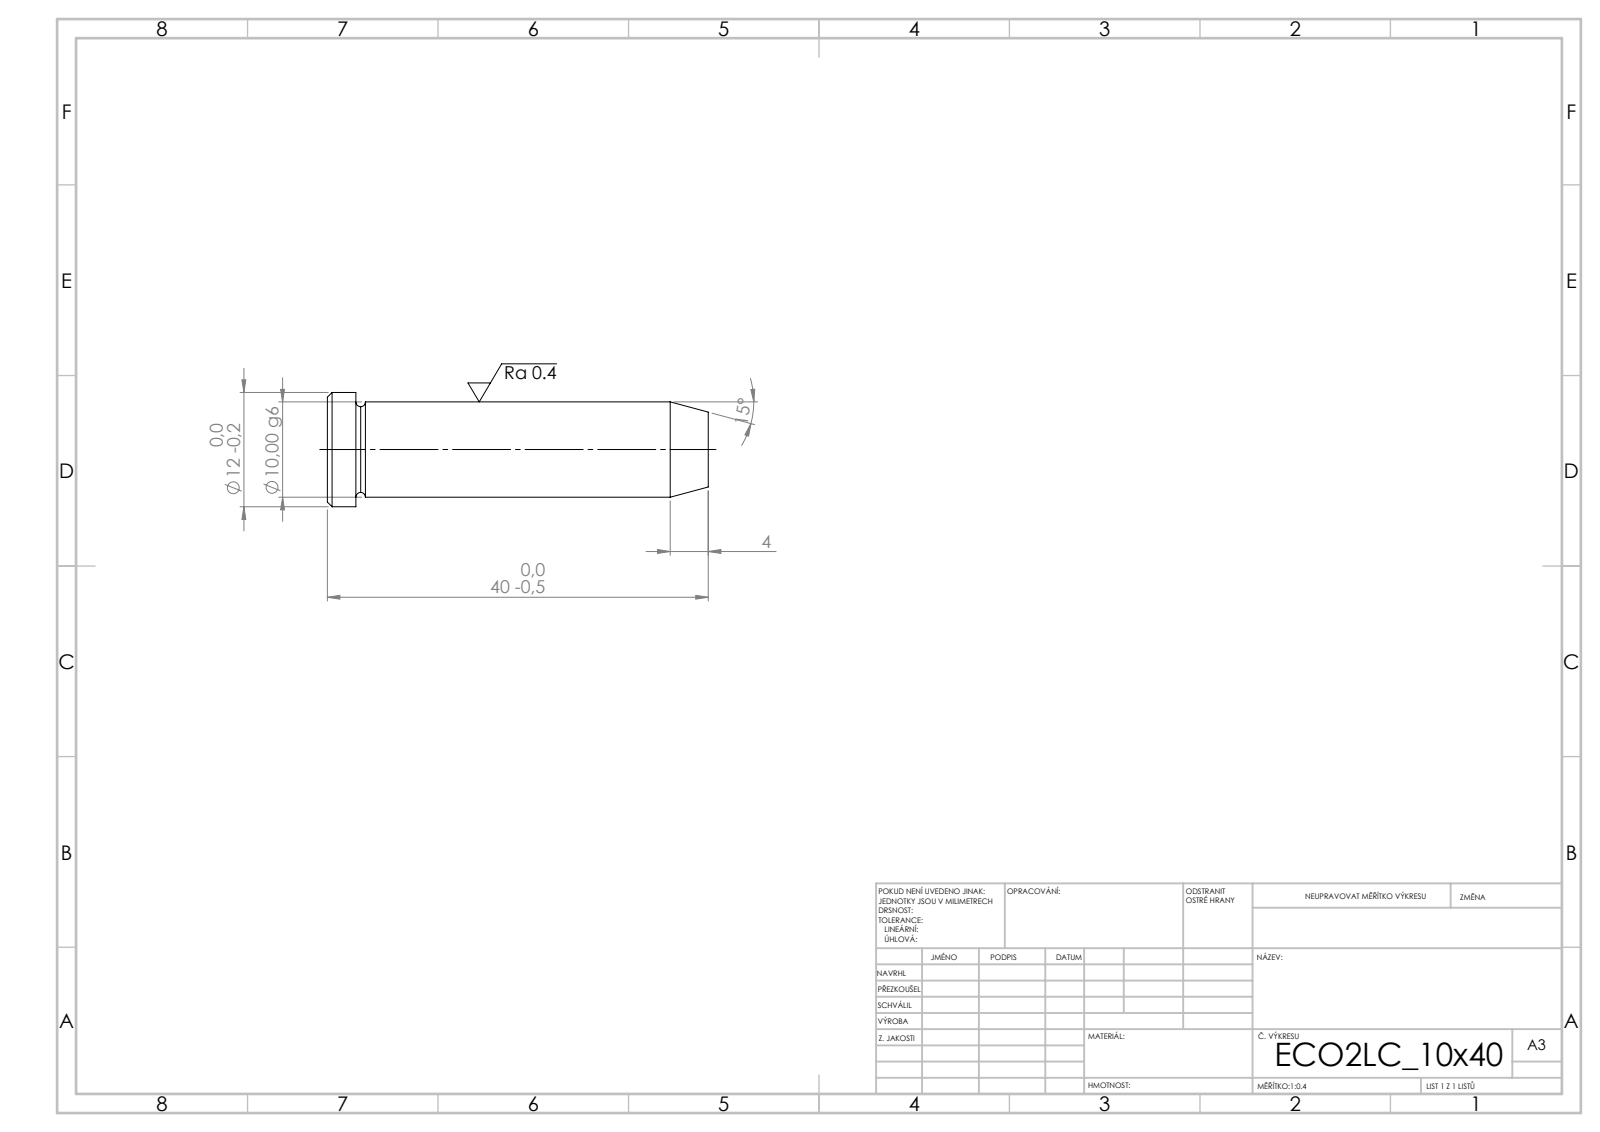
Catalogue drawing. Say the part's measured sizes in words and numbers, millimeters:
Its 3-D file was written by "SolidWorks 2019 (CONFIG_CONTROL_DESIGN)". It is 1 solid with 15 faces: 3 planar, 4 cylindrical and 8 other. Overall it measures 40 by 12 by 12 millimeters. Its volume is 3 166 cubic millimeters and its surface area 1 466 square millimeters. Round bosses or shafts: 1 of diameter 12, 1 of diameter 10. The main face-to-face distances are 40, 37, 3.
